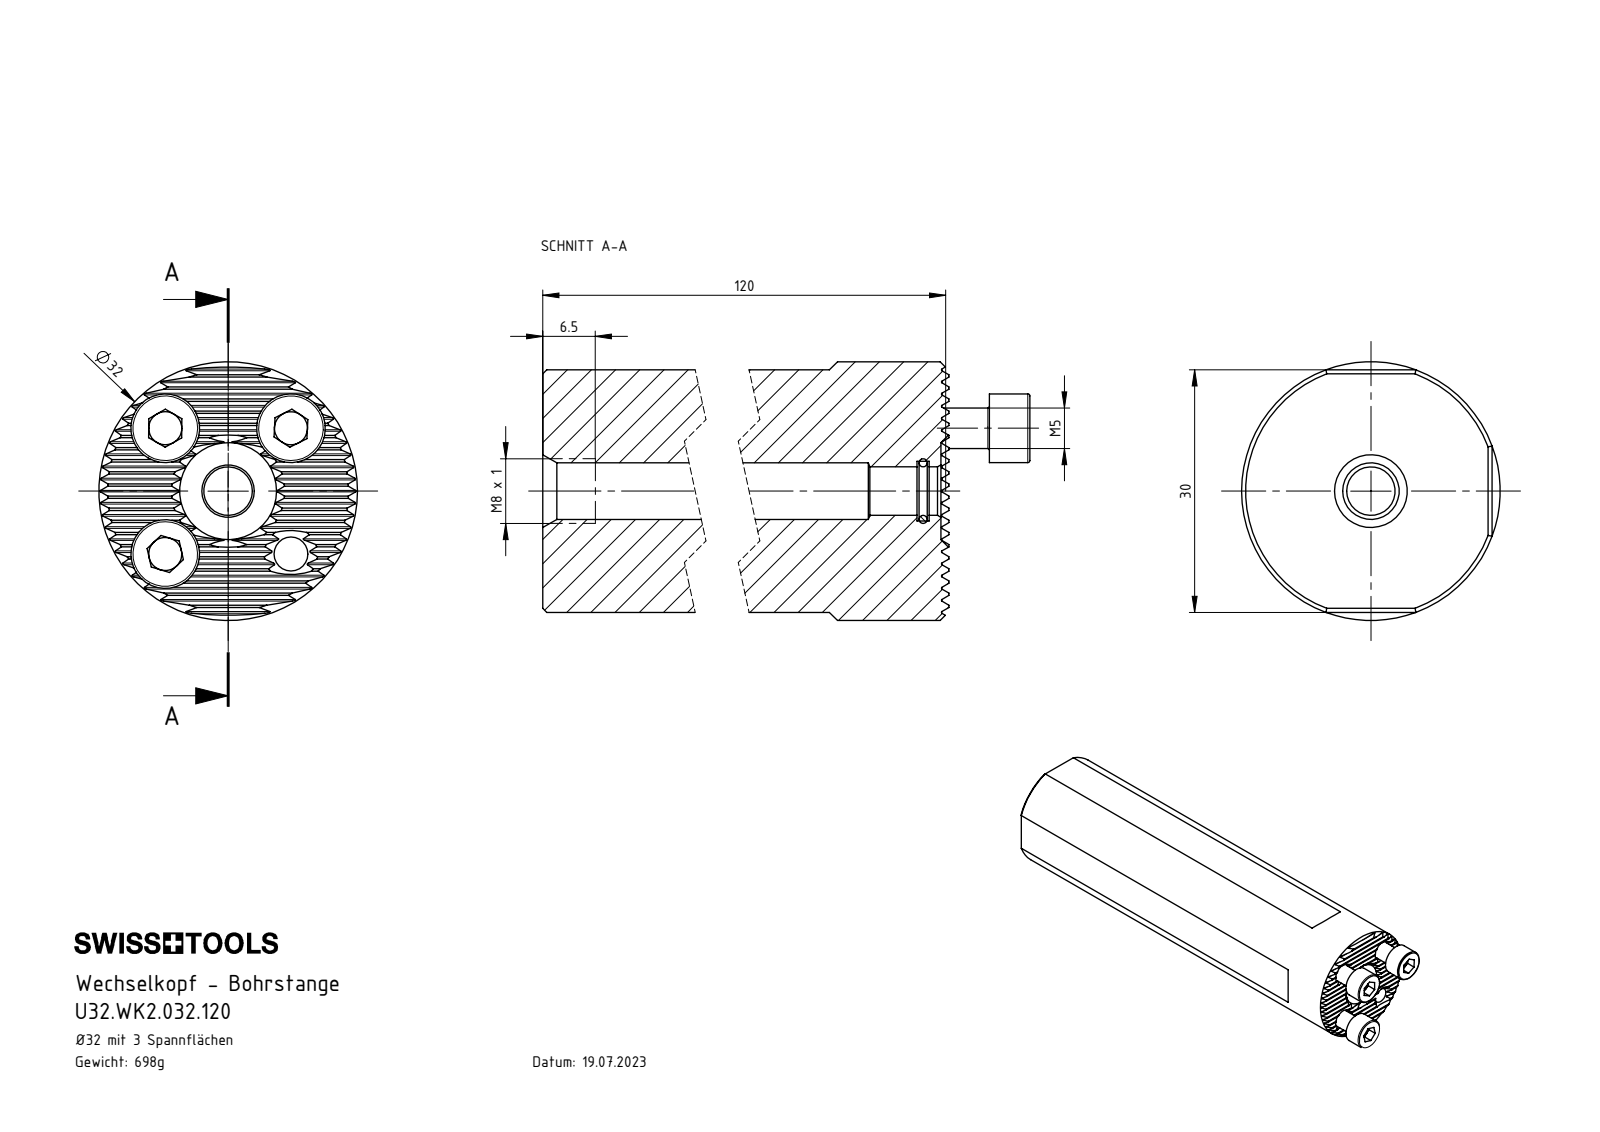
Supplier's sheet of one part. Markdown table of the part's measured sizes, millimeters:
| quantity | value |
| --- | --- |
| part name | DIN 3771 - 6x1; U32-WK2.032.120_A; ISO 4762 - M5 x 14; U32.WK2.032.120 |
| STEP written by | SolidWorks 2017 (AUTOMOTIVE_DESIGN) |
| units | millimeters |
| bodies | 5 solids, 318 faces (188 planar, 72 cylindrical, 58 other) |
| overall size | 130.4 × 32 × 32 |
| volume | 90 233 mm³ |
| surface area | 18 682 mm² |
| round holes (diameter × count) | 4.2 × 4, 6 × 1, 7 × 1, 7.4 × 1 |
| round bosses / shafts (diameter × count) | 8.5 × 3, 5 × 3, 32 × 1 |
| partial cylindrical surfaces (radius × count) | 0.12 × 21 |
| main face-to-face distances | 30, 1.3, 2.6, 3.9, 5.2, 12.99, 6.5, 11.69, 14.29, 10.39 |
| hole center spacings | 11, 15.56, 22.01 |
